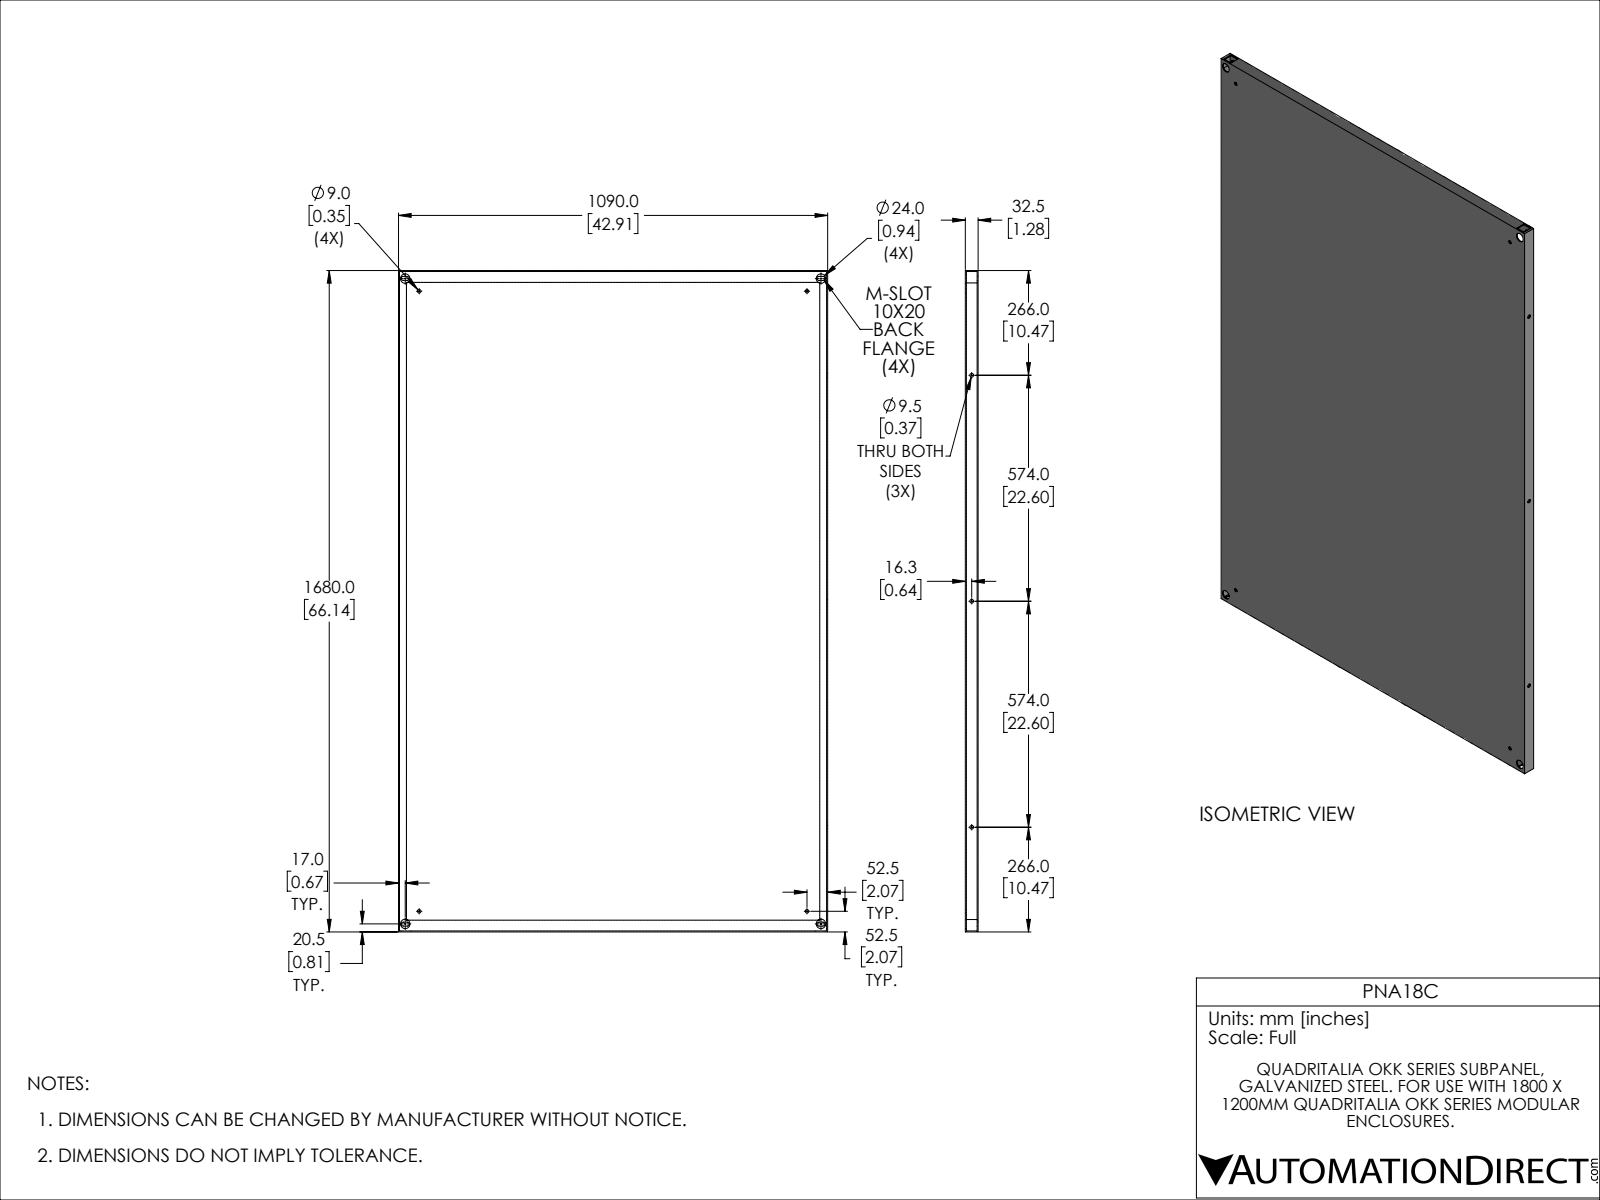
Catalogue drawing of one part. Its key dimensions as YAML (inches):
part_name: "PNA18C"
step_written_by: "SolidWorks 2021 (CONFIG_CONTROL_DESIGN)"
units: inches
bodies: {solids: 1, faces: 70, planar: 48, cylindrical: 22, other: 0}
overall_size: [66.142, 42.913, 1.28]
volume: 321.6
surface_area: 6560
round_holes:
  - {diameter: 0.354, count: 4}
  - {diameter: 0.945, count: 4}
  - {diameter: 0.374, count: 3}
partial_cylinders:
  - {radius: 0.197, count: 8}
face_to_face_distances: [0.098, 1.181, 1.28, 1.083, 42.815, 66.043, 42.913, 42.717, 66.142, 65.945]
hole_center_spacings: [1.881, 40.197, 63.283, 74.947, 22.598, 38.78, 41.575, 62.008]
